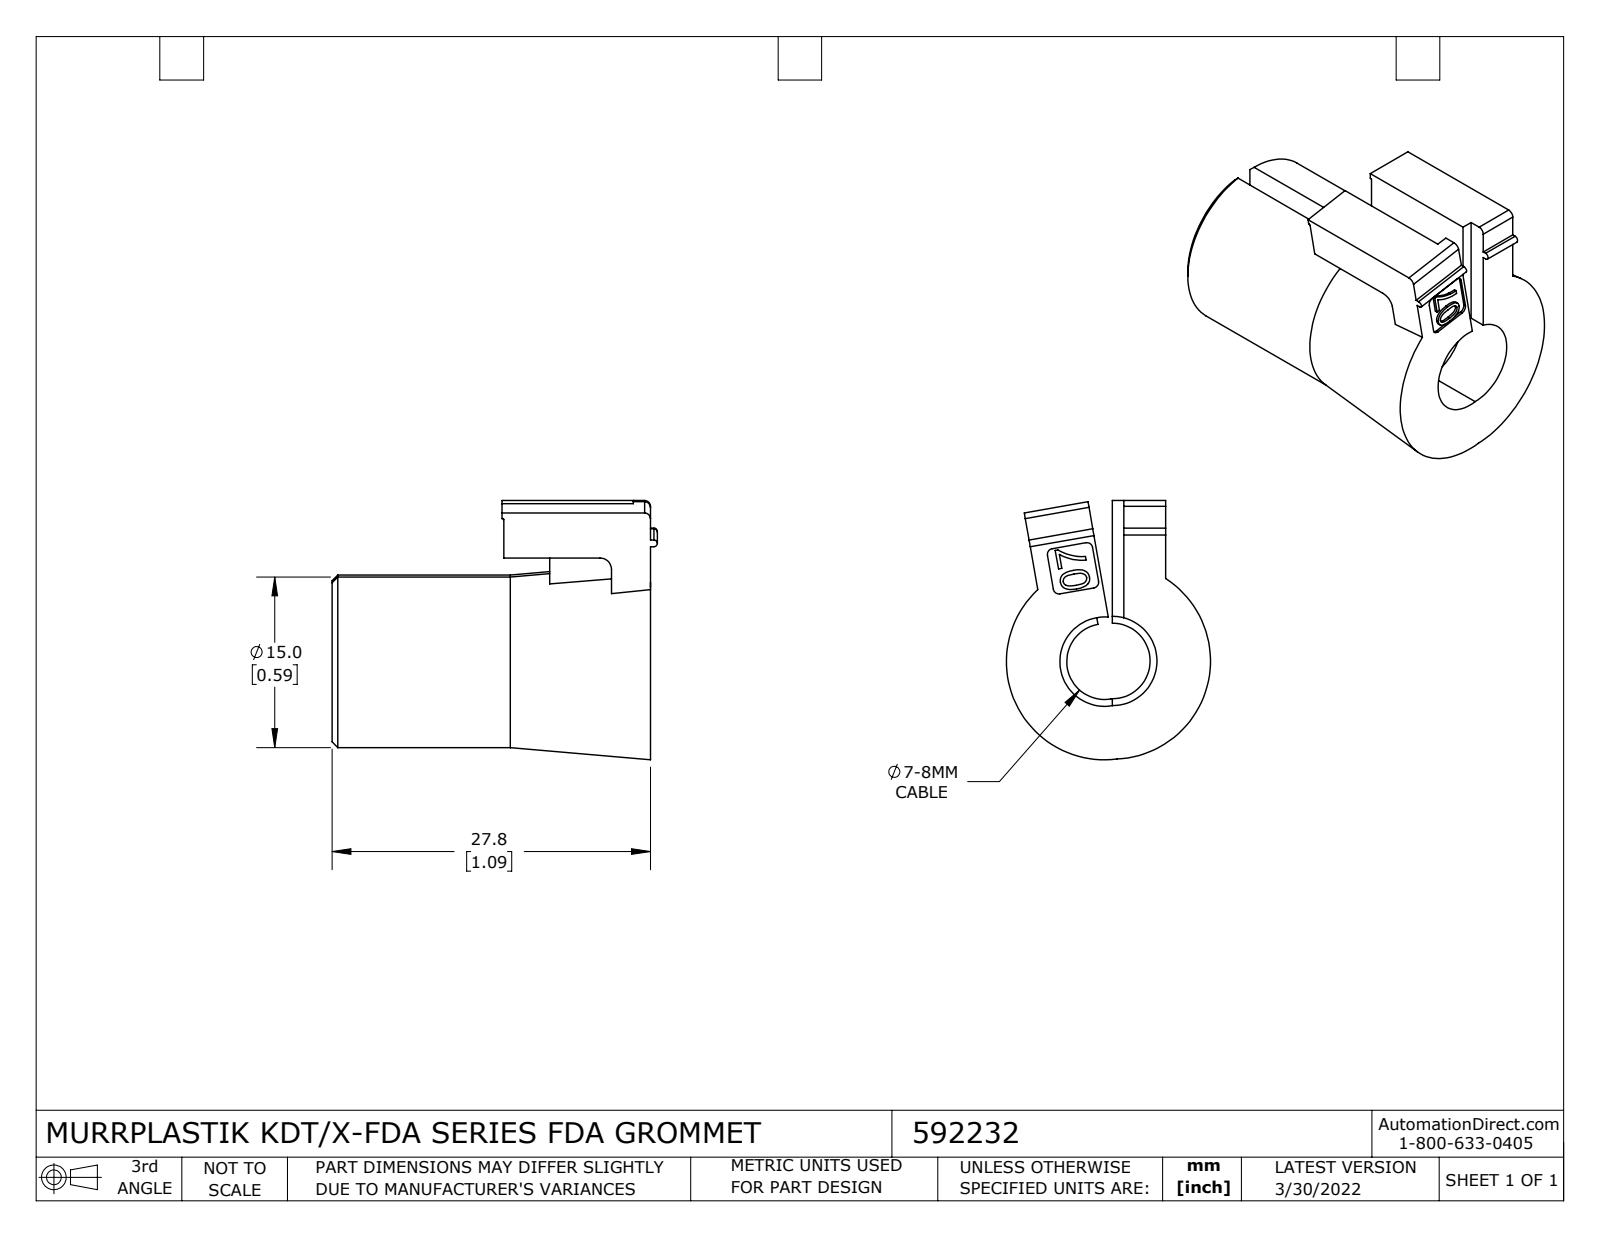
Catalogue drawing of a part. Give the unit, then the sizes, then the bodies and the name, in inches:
Units: inches
Overall size (bounding box): 1.118 × 0.891 × 0.701
Partial cylindrical surfaces — rounded edges, fillets, slot ends (radius × count): R0.02 ×6, R0.004 ×2, R0.012 ×2, R0.039 ×2, R0.13 ×2, R0.154 ×2, R0.295 ×2
Main face-to-face distances: 1.094, 0.157, 0.183, 0.183, 0.504, 0.591, 0.059, 0.445, 1.035, 0.039
Volume: 0.274 in³ · Surface area: 4.783 in²
Bodies: 1 solid, 107 faces (57 planar, 24 cylindrical, 26 other)
Part name (STEP PRODUCT): 592232
STEP written by: SolidWorks 2021 (CONFIG_CONTROL_DESIGN)
